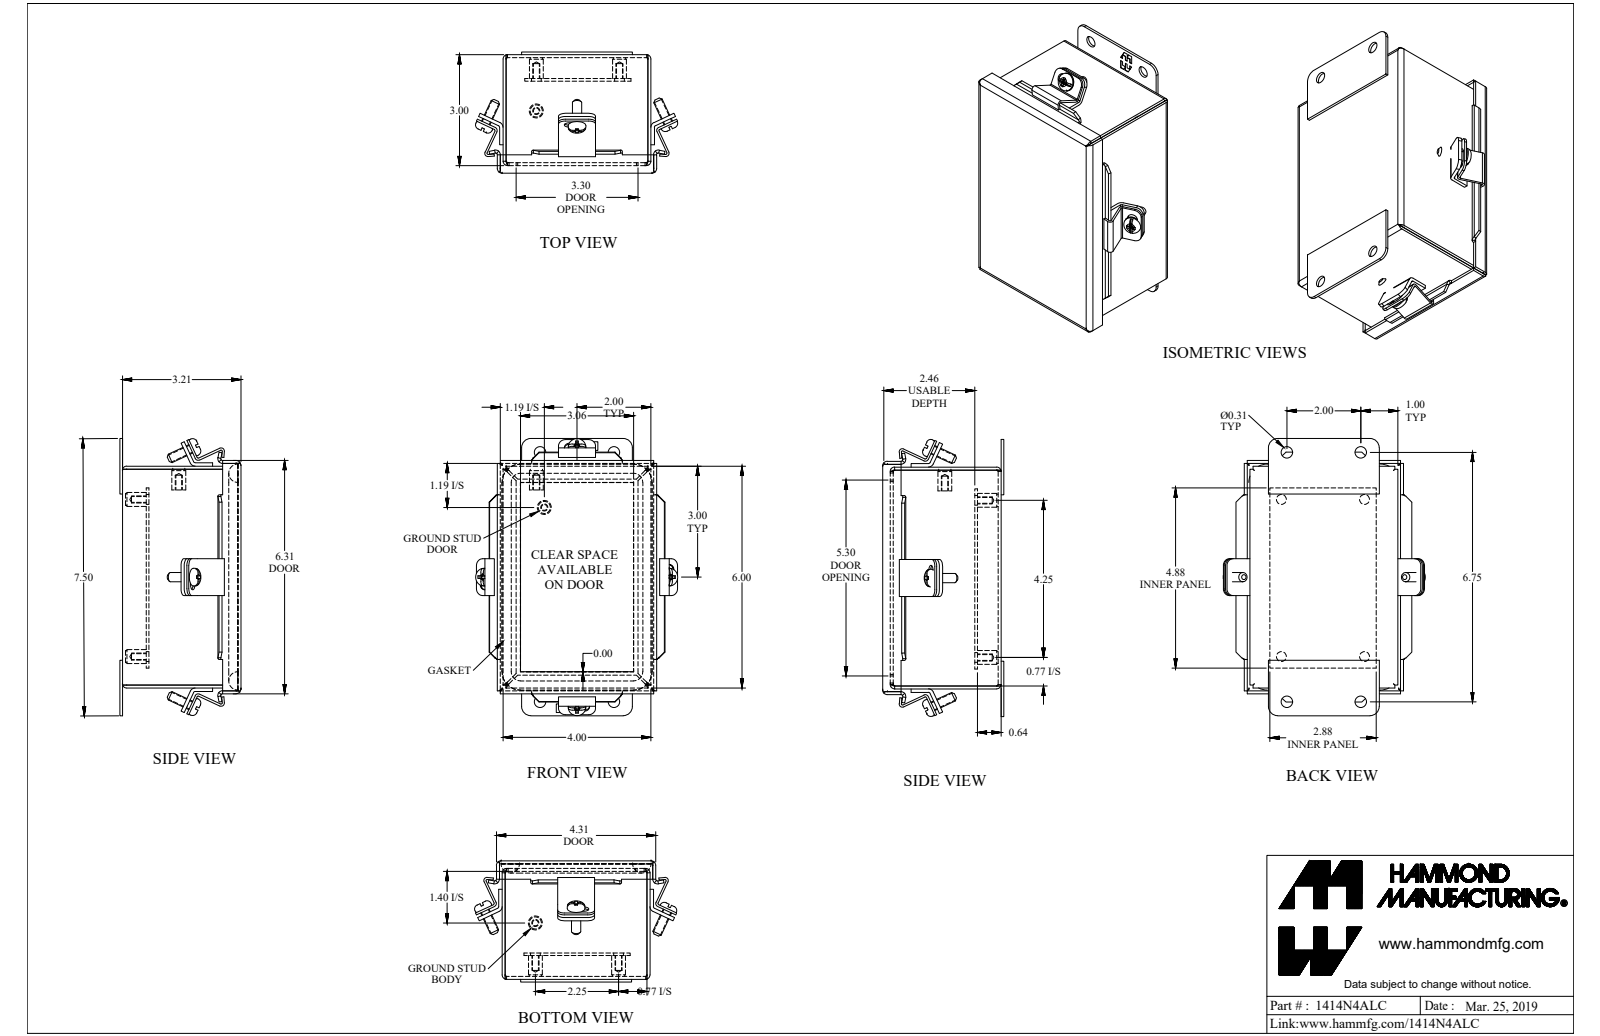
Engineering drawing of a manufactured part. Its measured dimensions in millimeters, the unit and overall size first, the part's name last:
Units: millimetres
Overall size (bounding box): 190.5 × 139 × 83.3
Round holes (diameter × count): ⌀4 ×6, ⌀5.4 ×4, ⌀6.7 ×4, ⌀8 ×4
Round bosses / shafts (diameter × count): ⌀8.4 ×6, ⌀12.2 ×4, ⌀6.4 ×4, ⌀9.5 ×3, ⌀9.5 ×3
Partial cylindrical surfaces — rounded edges, fillets, slot ends (radius × count): R0.3 ×8, R0.7 ×8, R0.9 ×8, R1.2 ×8, R2.2 ×8, R3 ×8, R3.6 ×8, R4.8 ×8
Main face-to-face distances: 2.1, 99.5, 79.4, 78.2, 3.3, 81.4, 1.8, 18.2, 150.3, 76.1
Hole centre spacings: 50.8, 57.2, 108, 122.1, 171.5, 178.8, 7.9, 31.3
Volume: 259 600 mm³ · Surface area: 241 700 mm²
Bodies: 24 solids, 673 faces (441 planar, 158 cylindrical, 74 other)
Part name (STEP PRODUCT): 1414N4ALC
STEP written by: SolidWorks 2018 (AUTOMOTIVE_DESIGN)
